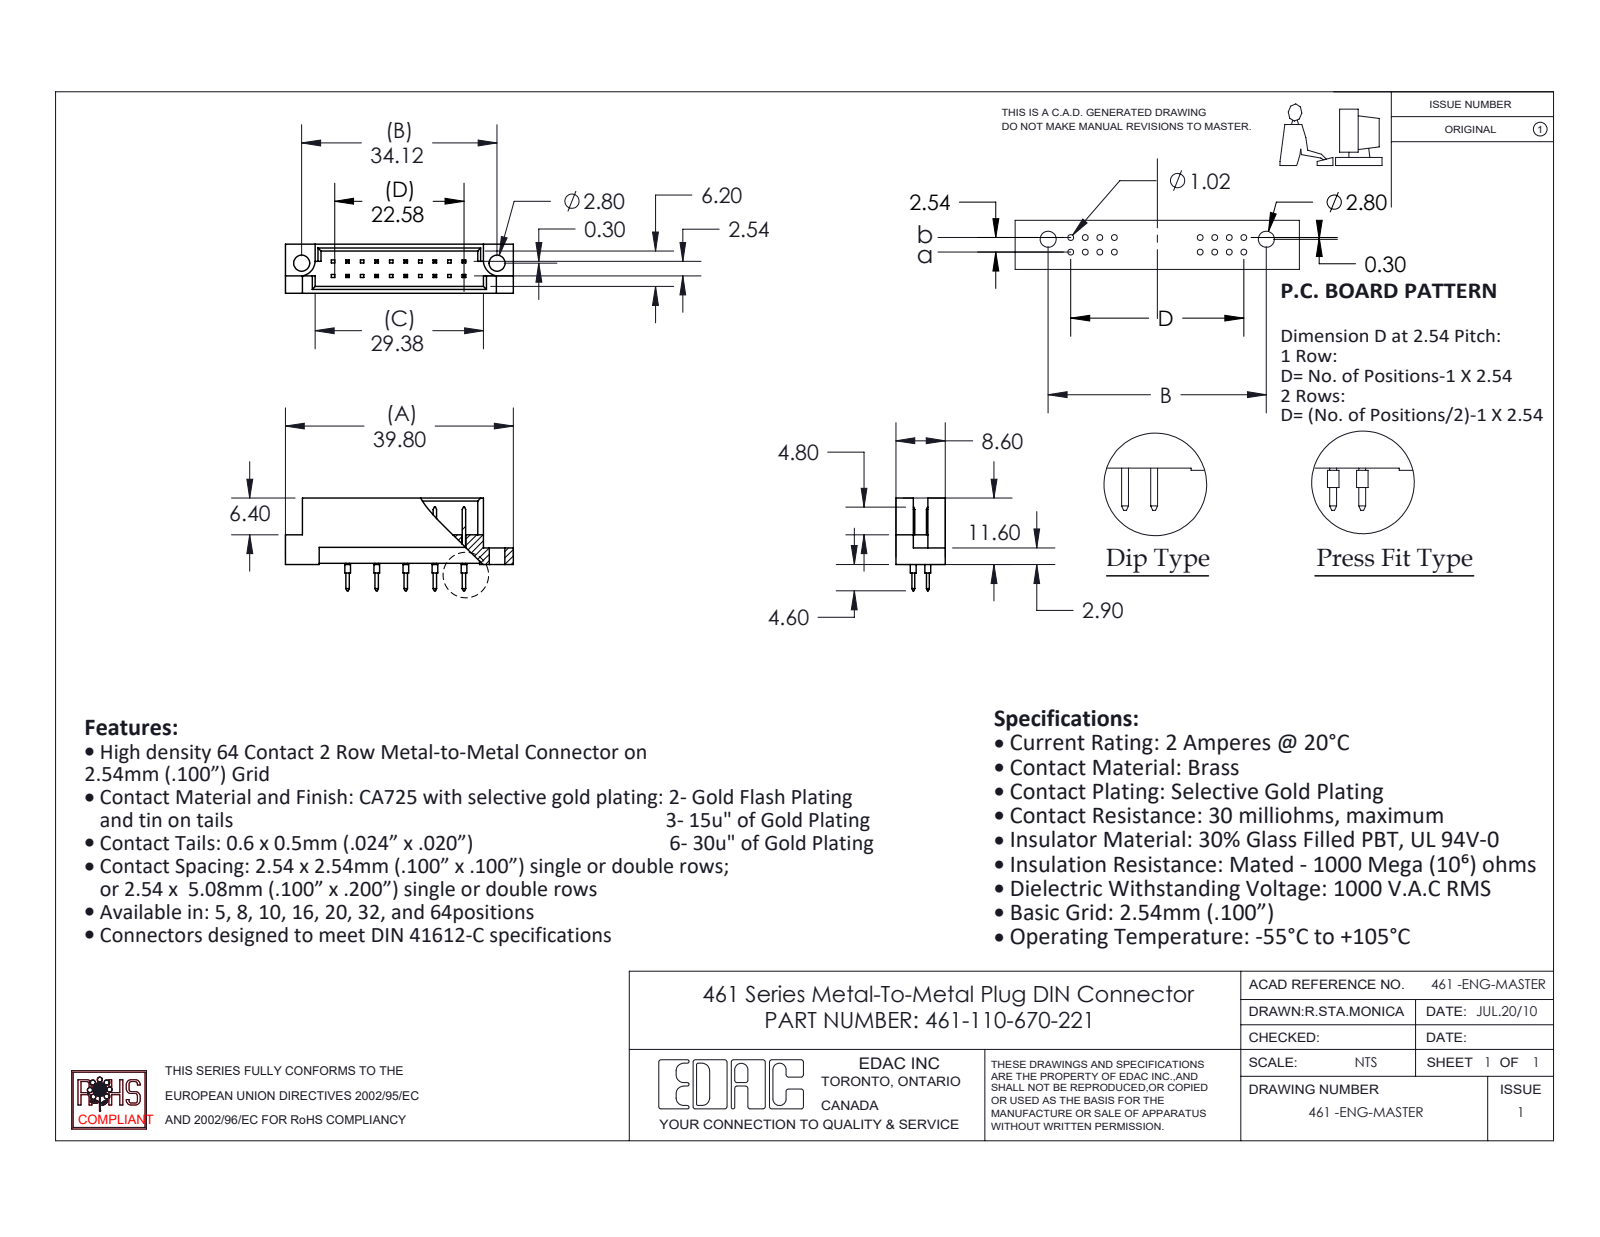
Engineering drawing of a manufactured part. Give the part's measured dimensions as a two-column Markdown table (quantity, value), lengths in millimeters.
| quantity | value |
| --- | --- |
| part name | 461 Part_20; 461-110-670-221; 461-290_70 |
| STEP written by | SolidWorks 2020 (CONFIG_CONTROL_DESIGN) |
| units | millimeters |
| bodies | 11 solids, 348 faces (322 planar, 26 cylindrical, 0 other) |
| overall size | 39.8 × 16.2 × 8.6 |
| volume | 1 955 mm³ |
| surface area | 2 679 mm² |
| round holes (diameter × count) | 2.8 × 2 |
| round bosses / shafts (diameter × count) | 1 × 10 |
| partial cylindrical surfaces (radius × count) | 2.8 × 2 |
| main face-to-face distances | 1.2, 7.4, 8.6, 6.2, 5, 2.54, 5.08, 1.58, 2.78, 3.28 |
| hole center spacings | 34.12 |
